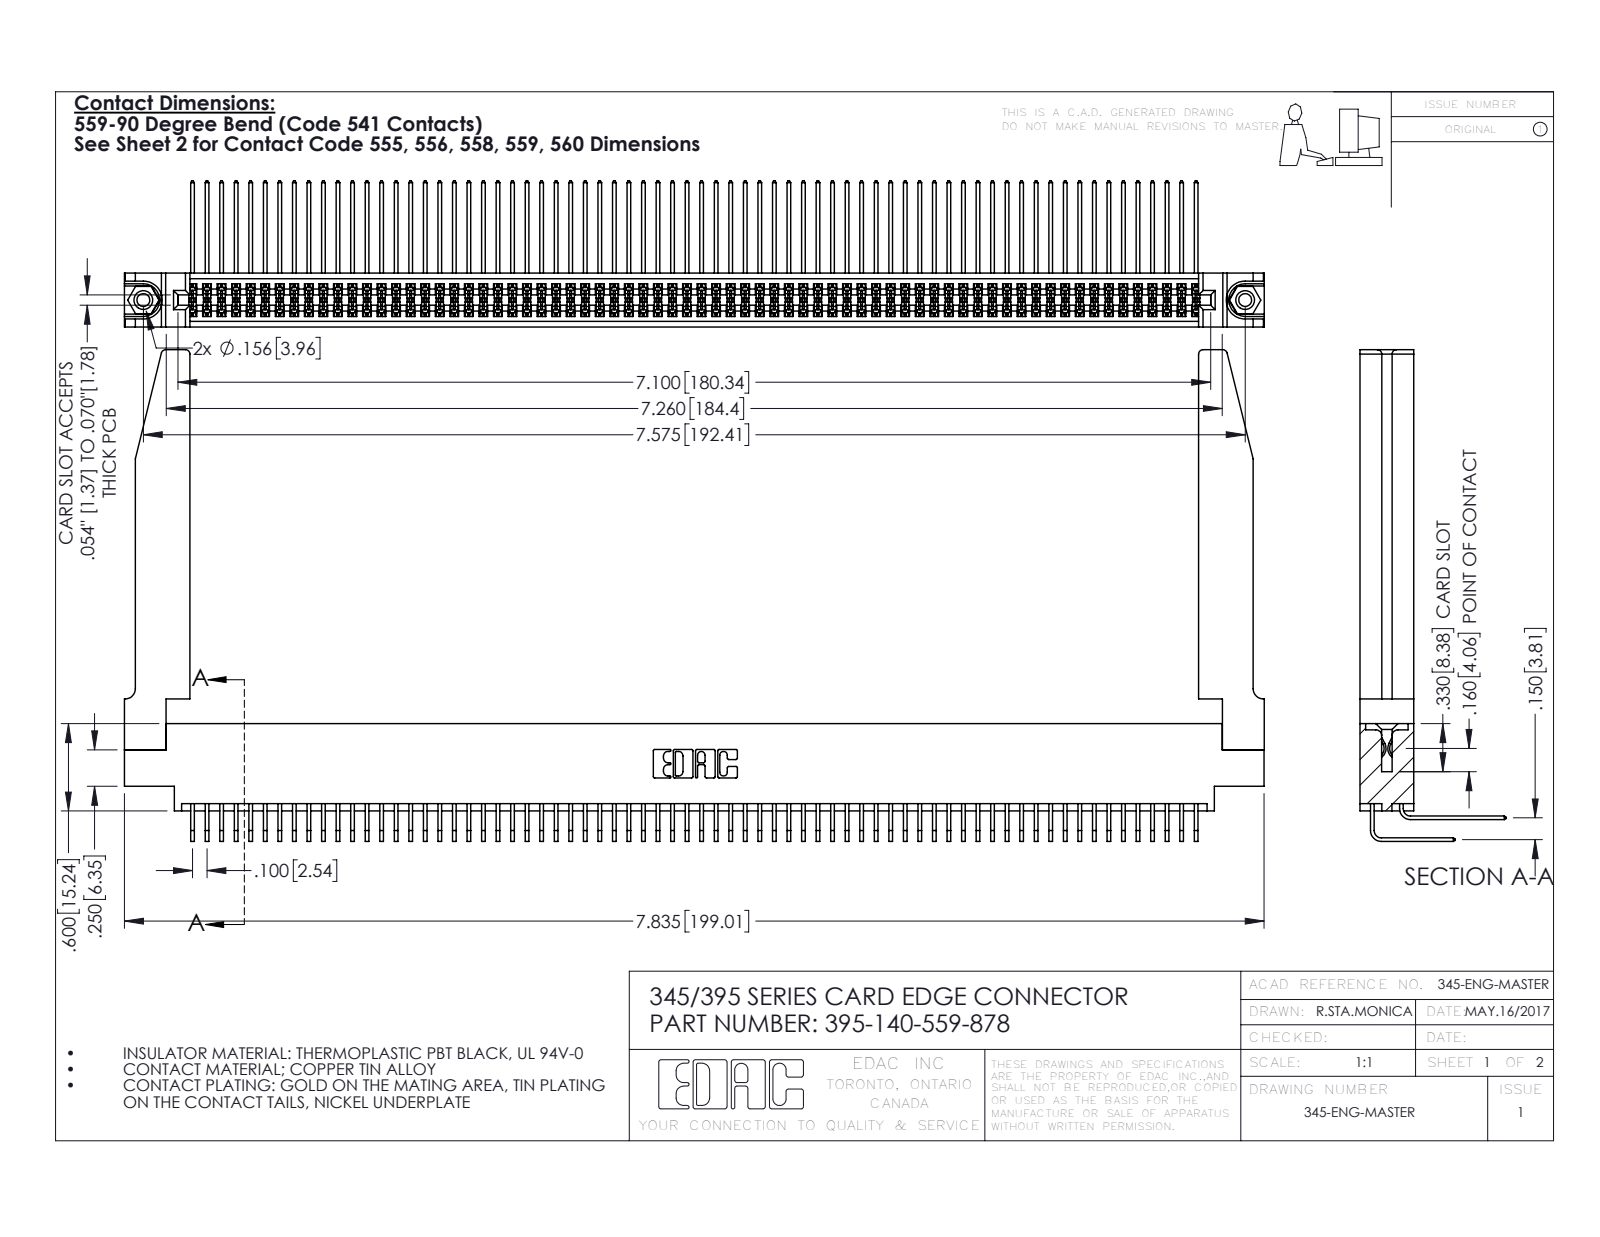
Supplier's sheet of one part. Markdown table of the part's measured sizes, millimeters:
| quantity | value |
| --- | --- |
| part name | 345-250-001_345-250-001-102; 345 Part_0.170 Offset - 0.156 Dia-TH; 395-140-559-878; 345-220-078_345-220-078 (+2 more) |
| STEP written by | SolidWorks 2016 (CONFIG_CONTROL_DESIGN) |
| units | millimeters |
| bodies | 145 solids, 7644 faces (5126 planar, 2466 cylindrical, 52 other) |
| overall size | 199 × 85.8 × 25.5 |
| volume | 28 050 mm³ |
| surface area | 41 310 mm² |
| round holes (diameter × count) | 2.3 × 2, 3.2 × 2, 4 × 2, 1.6 × 1 |
| round bosses / shafts (diameter × count) | 3.9 × 2 |
| partial cylindrical surfaces (radius × count) | 0.2 × 279, 0.3 × 22, 0.8 × 8, 0.2 × 6, 0.8 × 6, 0.7 × 3, 0.4 × 2, 0.5 × 2 |
| main face-to-face distances | 1.8, 7.6, 9.4, 2.5, 6.9, 0.6, 5.1, 5.7, 4.4, 3.8 |
| hole center spacings | 6.9, 186.4, 192.4 |
